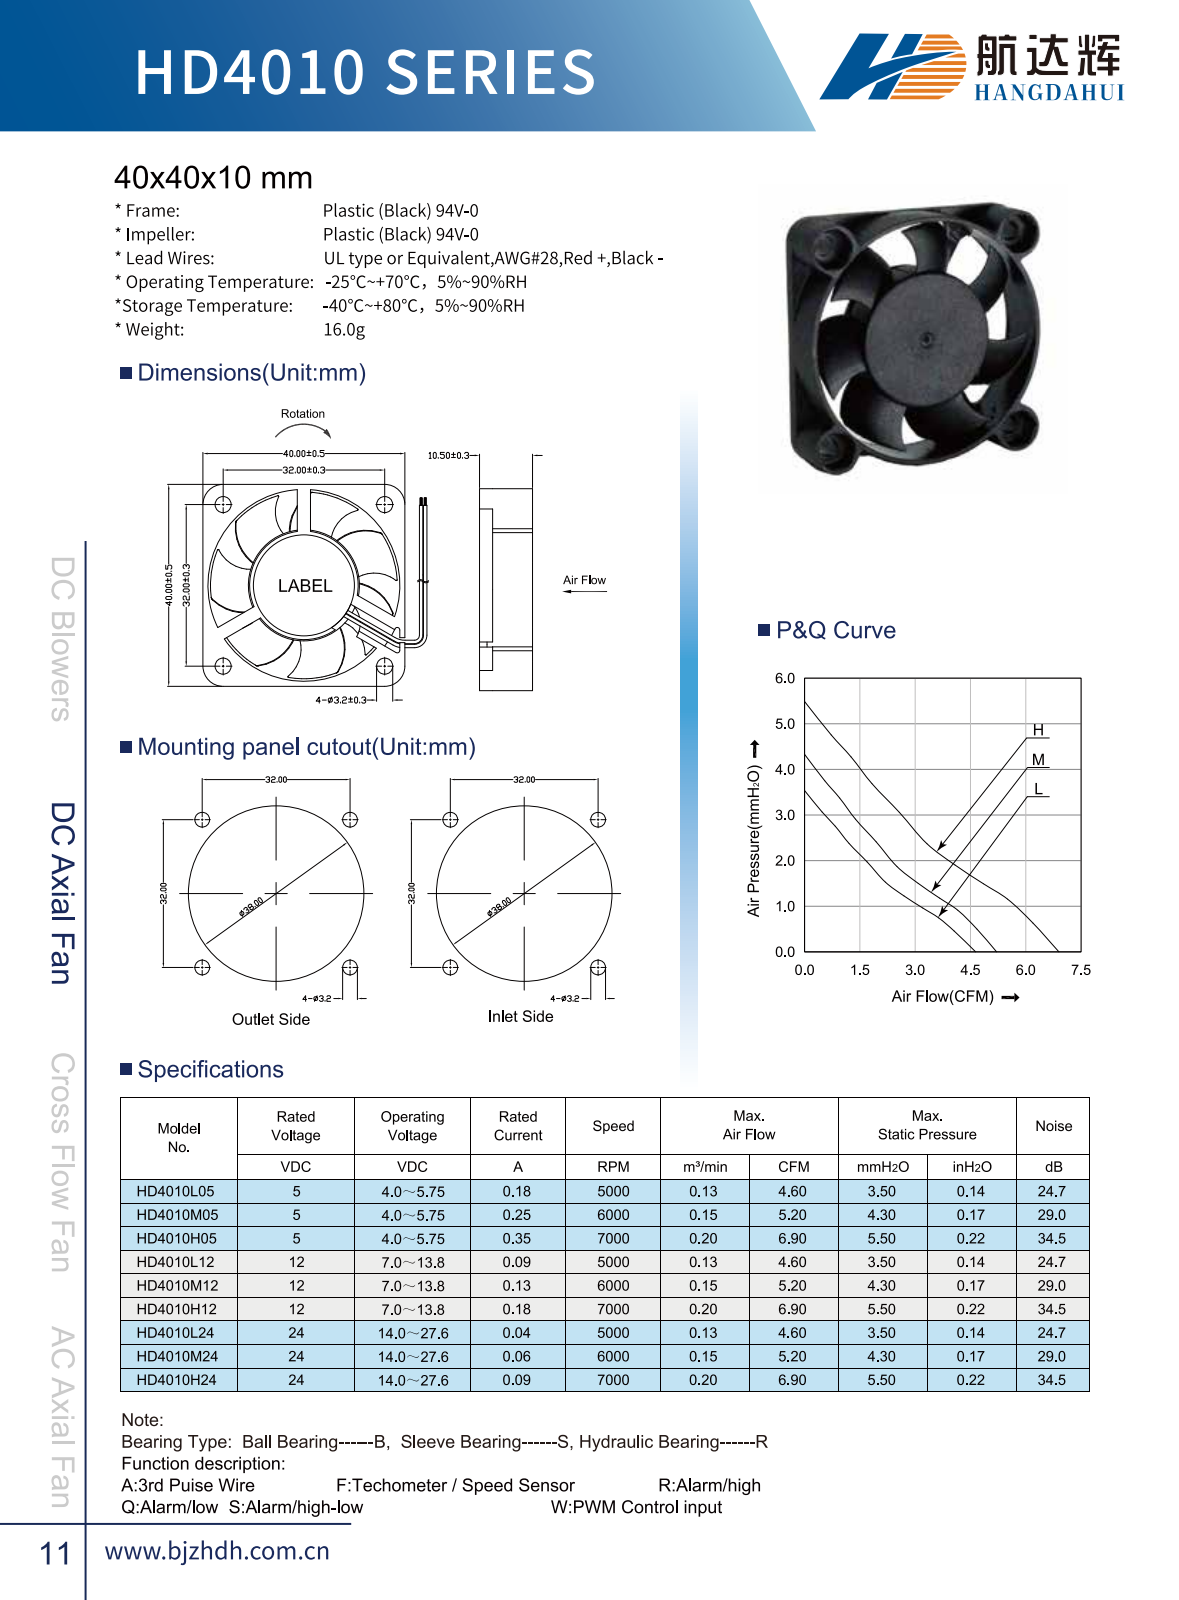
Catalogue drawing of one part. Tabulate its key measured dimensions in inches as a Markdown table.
| quantity | value |
| --- | --- |
| part name | 401000; 4010000; 401000_ASM |
| STEP written by | CREO PARAMETRIC BY PTC INC, 2019010 (CONFIG_CONTROL_DESIGN) |
| units | inches |
| bodies | 2 solids, 231 faces (69 planar, 77 cylindrical, 85 other) |
| overall size | 1.575 × 1.575 × 0.417 |
| volume | 0.292 in³ |
| surface area | 13.31 in² |
| round holes (diameter × count) | 0.126 × 4, 0.785 × 1, 0.803 × 1, 1.496 × 1 |
| round bosses / shafts (diameter × count) | 0.827 × 1, 0.252 × 1, 0.157 × 1, 0.078 × 1 |
| partial cylindrical surfaces (radius × count) | 0.039 × 15, 0.02 × 9, 0.079 × 6, 0.152 × 4, 0.157 × 4, 0.012 × 1, 0.098 × 1, 0.425 × 1 |
| main face-to-face distances | 0.417, 0.047, 0.051, 0.37, 0.319, 0.366, 0.028, 0.055, 0.213, 0.102 |
| hole center spacings | 0.891, 1.26, 1.781 |
